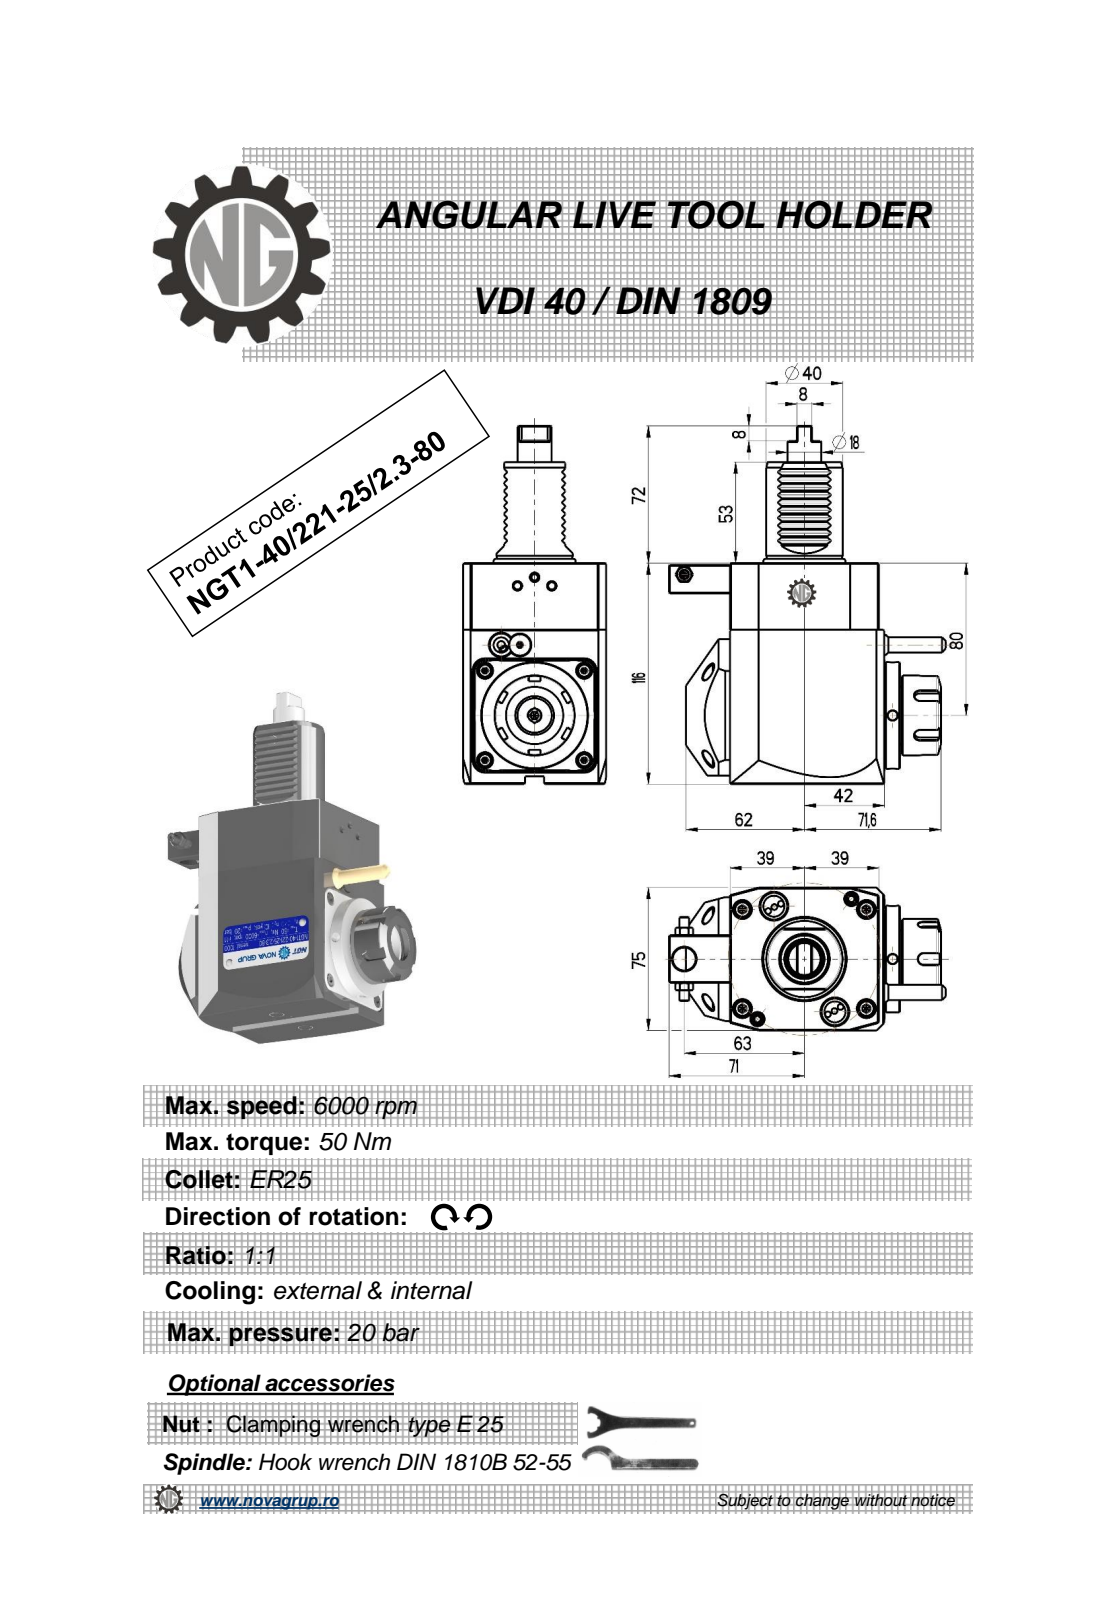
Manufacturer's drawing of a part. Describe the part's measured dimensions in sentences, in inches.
The part is named "NGT1_40_221_25_2_3_80". Its 3-D file was written by "PRO/ENGINEER BY PARAMETRIC TECHNOLOGY CORPORATION, 2010280 (CONFIG_CONTROL_DESIGN)". It is 1 solid with 471 faces: 228 planar, 94 cylindrical and 149 other. Overall it measures 7.402 by 5.714 by 2.953 inches. Its volume is 52.91 cubic inches and its surface area 109.5 square inches. Round holes: 3 of diameter 0.197, 1 of diameter 0.118, 1 of diameter 0.165, 1 of diameter 0.374, 1 of diameter 0.472, 1 of diameter 0.799. Round bosses or shafts: 1 of diameter 2.205, 1 of diameter 1.693, 1 of diameter 1.654, 1 of diameter 1.575, 1 of diameter 1.299, 1 of diameter 0.701, 1 of diameter 0.441, 1 of diameter 0.353. Partial cylindrical surfaces (rounded edges, fillets, slot ends): 20 of radius 0.012, 12 of radius 0.01, 6 of radius 0.009, 5 of radius 0.118, 2 of radius 0.031, 1 of radius 1.575. The main face-to-face distances are 2.953, 4.567, 3.189, 3.071, 0.118, 0.433, 0.315, 3.181, 0.11, 4.409. The hole center spacings are 1.558, 1.611, 2.854, 4.301, 5.195.
